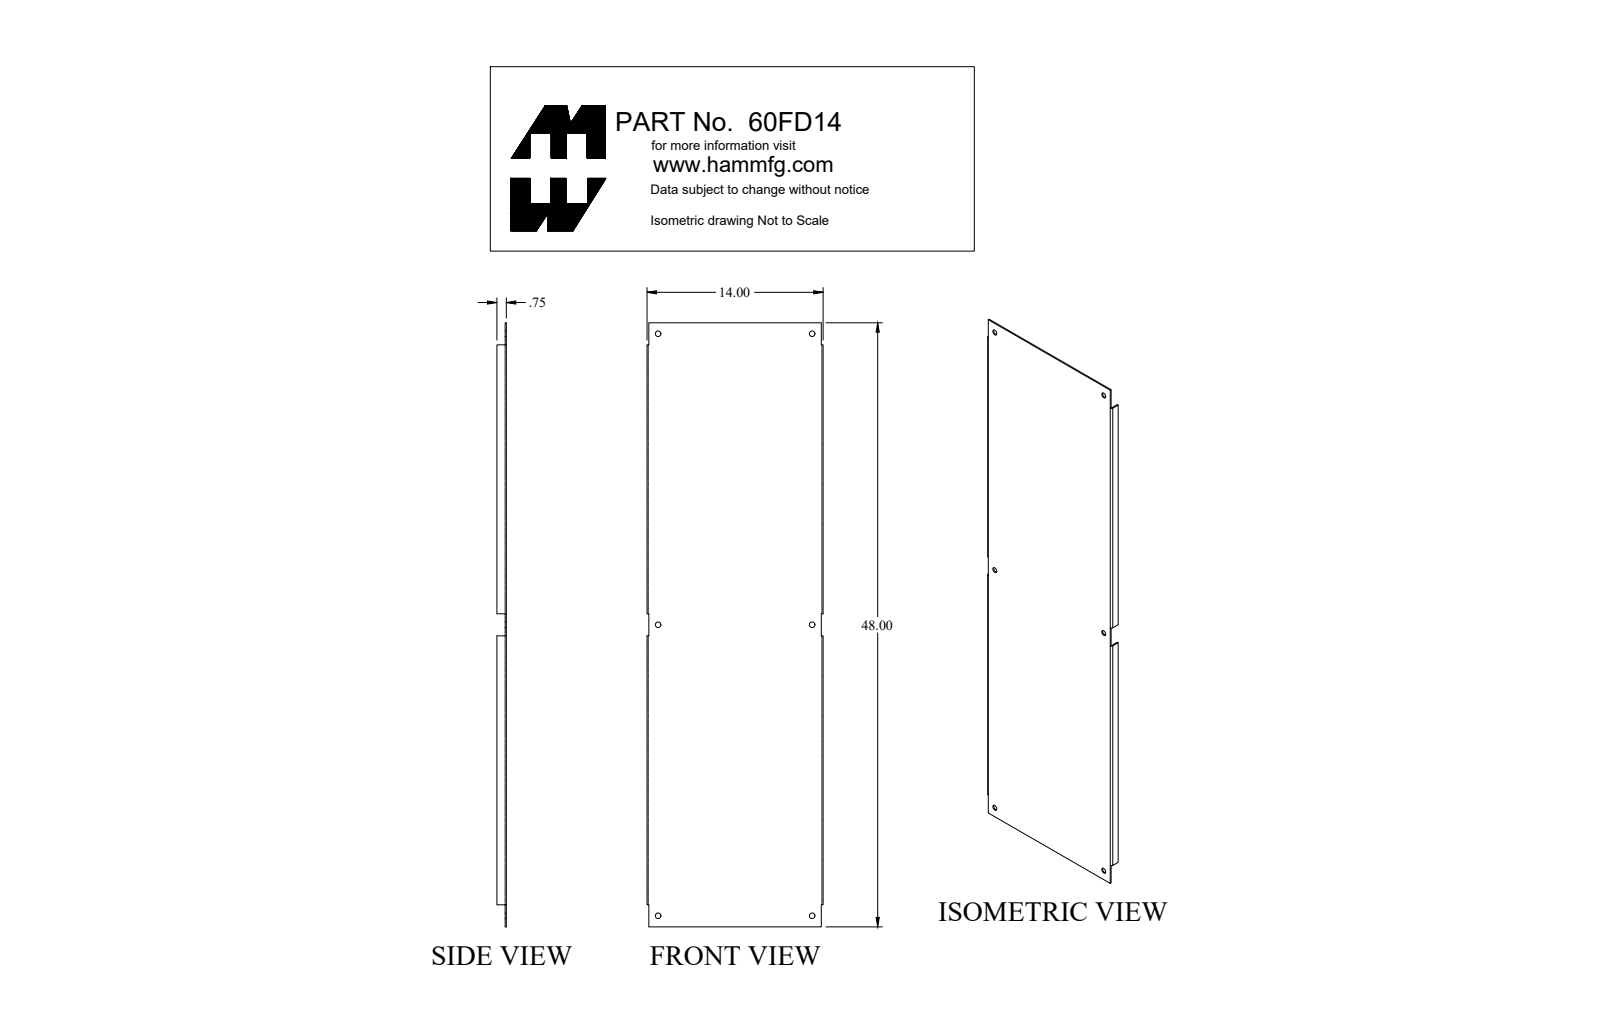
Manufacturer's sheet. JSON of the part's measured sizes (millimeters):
{"part_name": "60FD14_Default", "step_written_by": "SolidWorks 2018 (CONFIG_CONTROL_DESIGN)", "units": "millimeters", "bodies": {"solids": 1, "faces": 6, "planar": 6, "cylindrical": 0, "other": 0}, "overall_size": [1520.7, 1215.9, 3.2], "volume_mm3": 5870000, "surface_area_mm2": 3715000, "face_to_face_distances": [3.2, 1215.9, 1520.7]}
